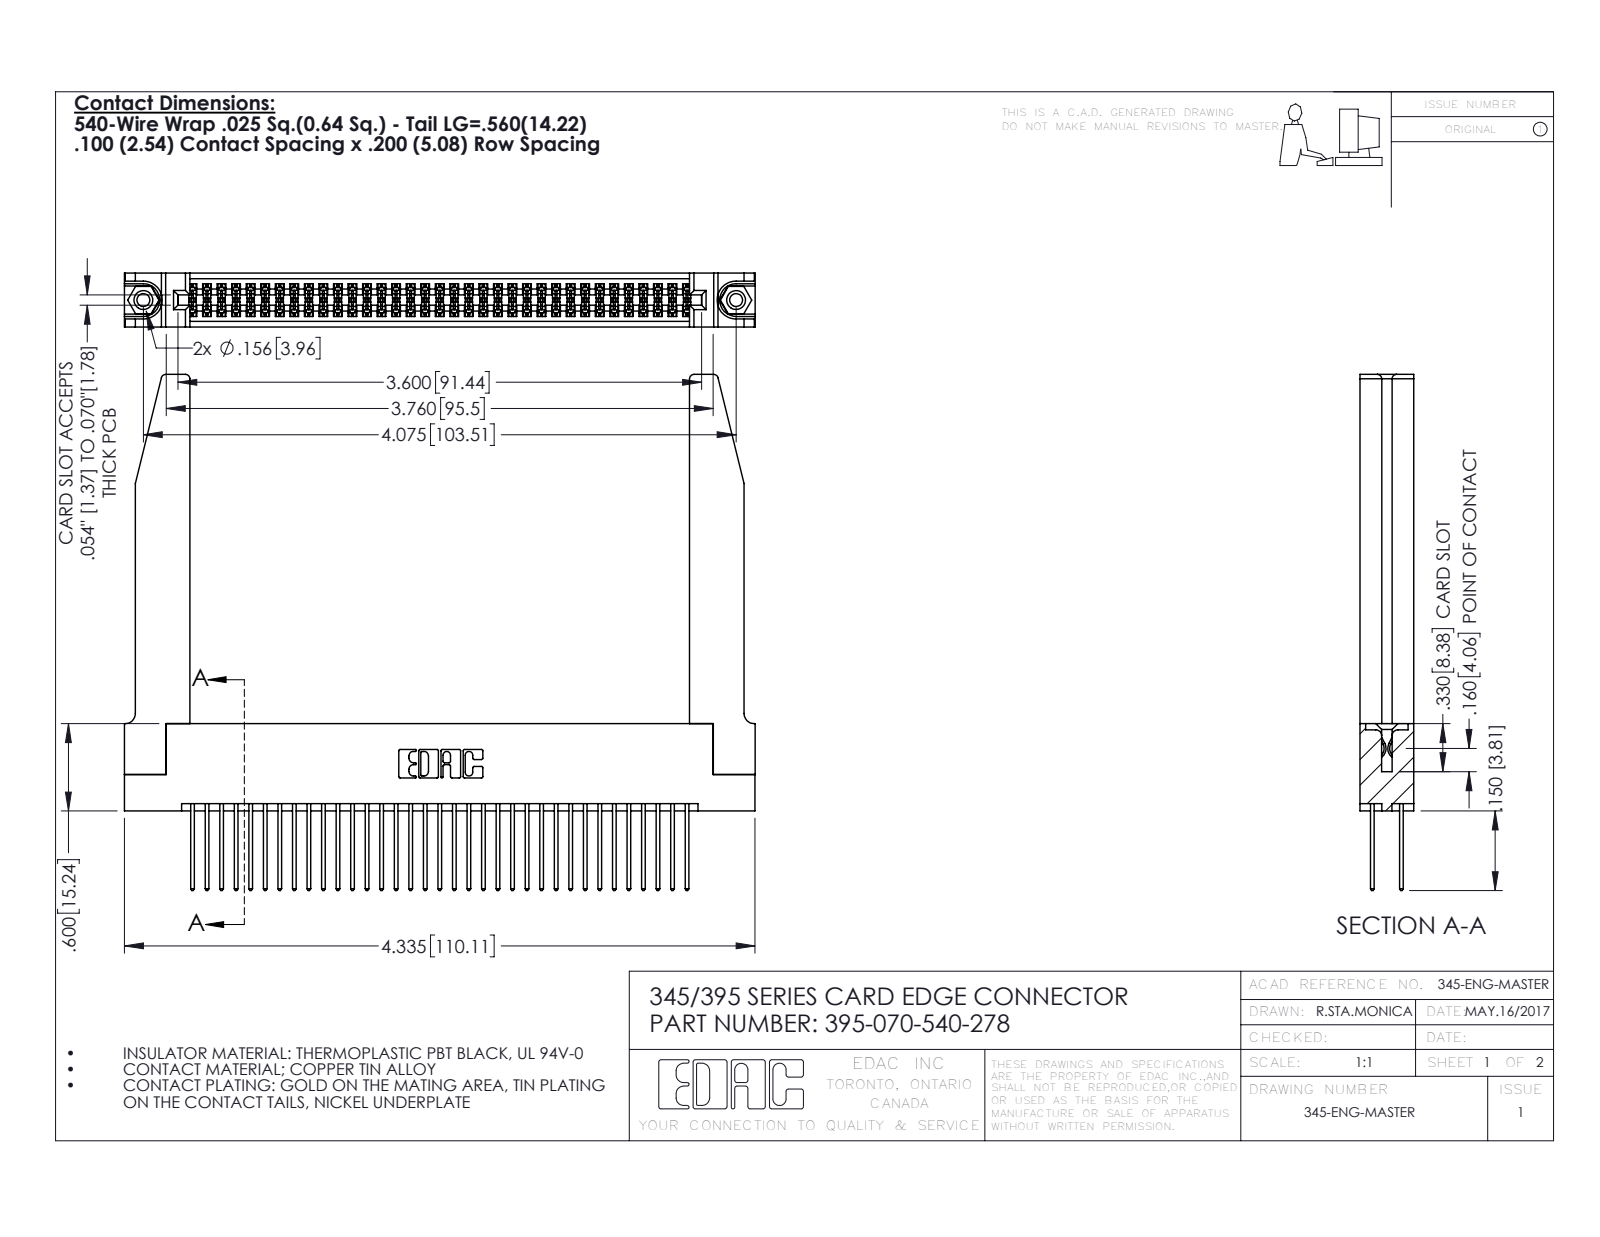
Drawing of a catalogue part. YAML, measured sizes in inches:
part_name: "395-070-540-278; 345 Part_Flush Mounting Lugs - 0.156 Dia-TH; 345-250-001_345-250-001-102; 345-292-001_345-293-140 (+1 more)"
step_written_by: "SolidWorks 2016 (CONFIG_CONTROL_DESIGN)"
units: inches
bodies: {solids: 75, faces: 3860, planar: 2532, cylindrical: 1276, other: 52}
overall_size: [4.336, 3.547, 0.37]
volume: 1.139
surface_area: 37.27
round_holes:
  - {diameter: 0.089, count: 2}
  - {diameter: 0.125, count: 2}
  - {diameter: 0.156, count: 2}
  - {diameter: 0.064, count: 1}
round_bosses_or_shafts:
  - {diameter: 0.155, count: 2}
partial_cylinders:
  - {radius: 0.006, count: 105}
  - {radius: 0.01, count: 70}
  - {radius: 0.01, count: 22}
  - {radius: 0.03, count: 8}
  - {radius: 0.007, count: 6}
  - {radius: 0.031, count: 6}
  - {radius: 0.026, count: 3}
  - {radius: 0.014, count: 2}
face_to_face_distances: [0.072, 0.298, 0.37, 0.2, 0.098, 0.272, 0.025, 0.225, 0.175, 0.148]
hole_center_spacings: [0.27, 3.839, 4.075]
